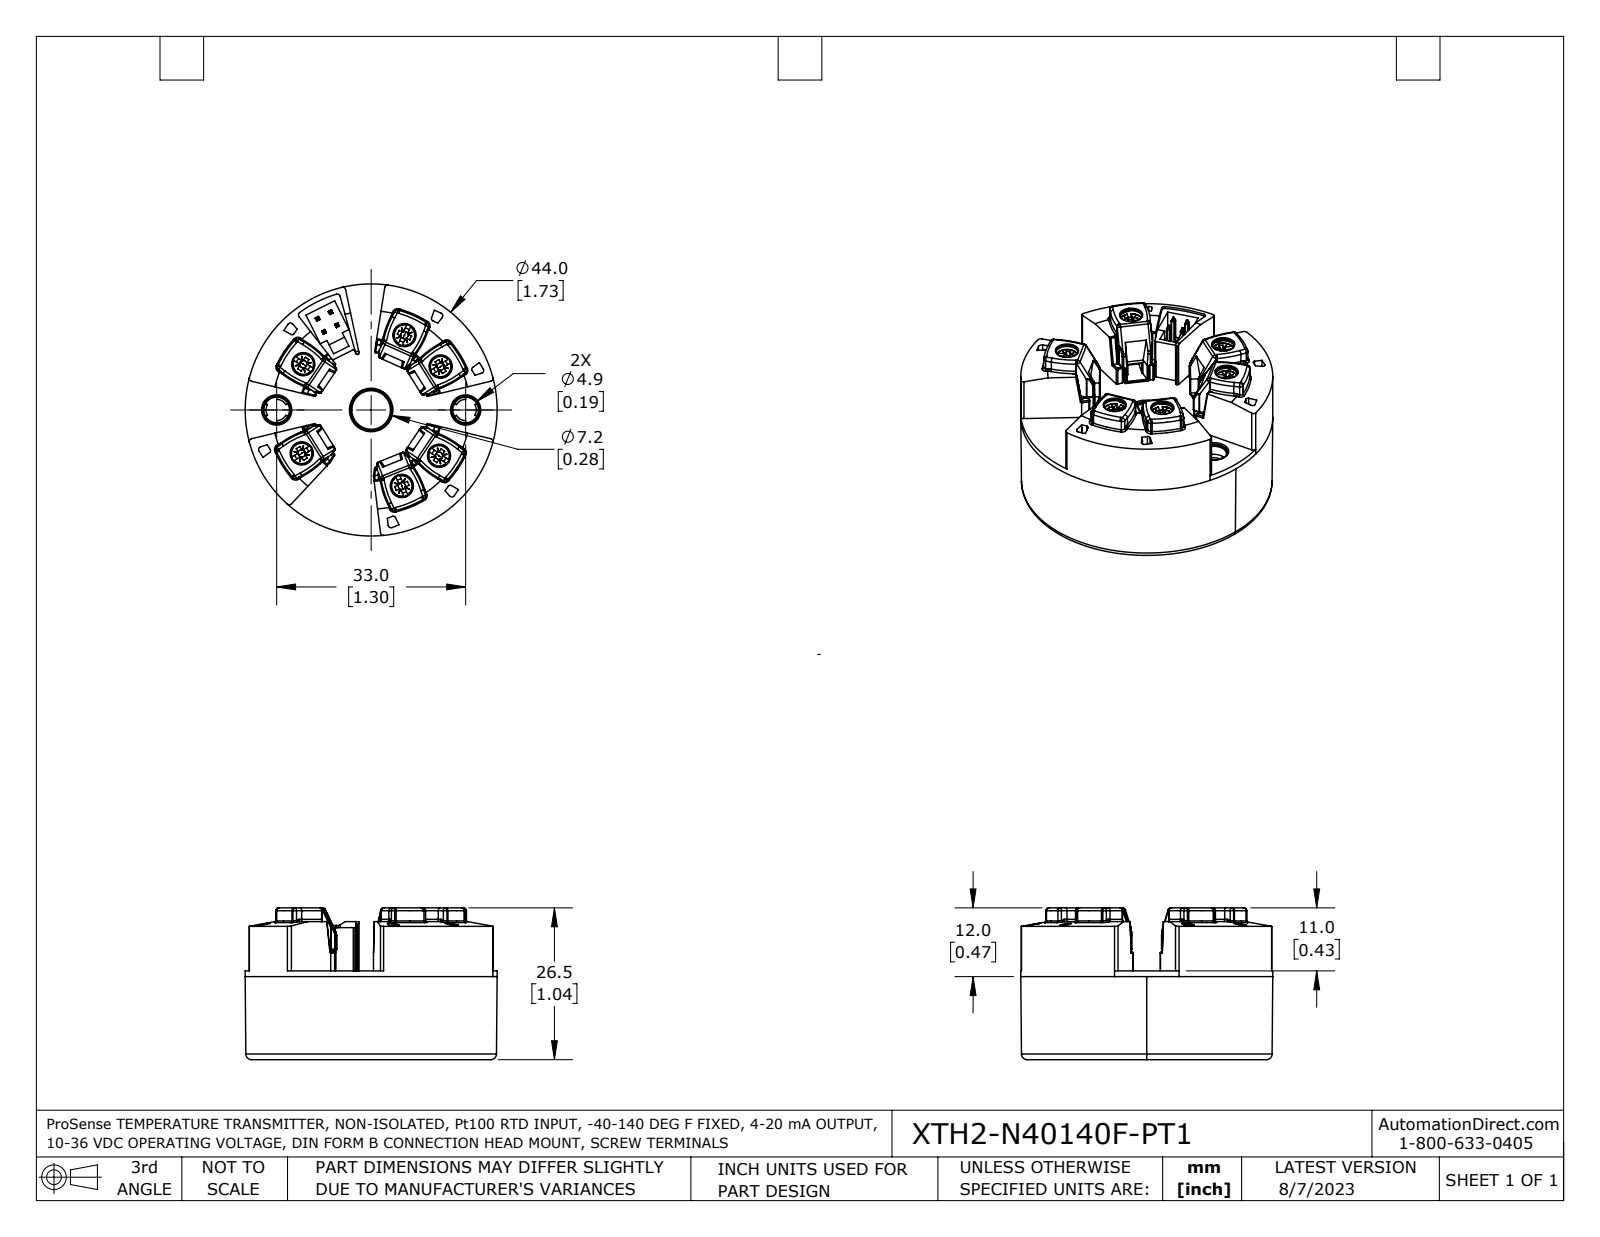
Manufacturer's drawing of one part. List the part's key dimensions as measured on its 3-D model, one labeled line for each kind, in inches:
Part name (STEP PRODUCT): XTH2-N40140F-PT1
STEP written by: SolidWorks 2021 (AUTOMOTIVE_DESIGN)
Units: inches
Bodies: 1 solid, 2500 faces (944 planar, 967 cylindrical, 589 other)
Overall size (bounding box): 1.732 × 1.732 × 1.043
Volume: 0.846 in³ · Surface area: 24.66 in²
Round holes (diameter × count): ⌀0.102 ×6, ⌀0.151 ×6, ⌀0.159 ×6, ⌀0.193 ×2, ⌀0.248 ×2, ⌀0.213 ×1, ⌀0.283 ×1, ⌀0.339 ×1, ⌀0.685 ×1
Round bosses / shafts (diameter × count): ⌀0.106 ×12, ⌀0.156 ×6, ⌀0.098 ×6, ⌀1.732 ×1, ⌀1.646 ×1, ⌀0.402 ×1
Partial cylindrical surfaces — rounded edges, fillets, slot ends (radius × count): R0.008 ×247, R0.02 ×144, R0.012 ×58, R0.004 ×48, R0.01 ×36, R0.006 ×18, R0.016 ×12, R0.592 ×12
Main face-to-face distances: 0.039, 0.571, 0.453, 0.118, 0.492, 0.61, 0.079, 0.531, 0.098, 0.067
Hole centre spacings: 0.563, 0.863, 0.329, 0.344, 0.364, 0.563, 0.613, 0.65
